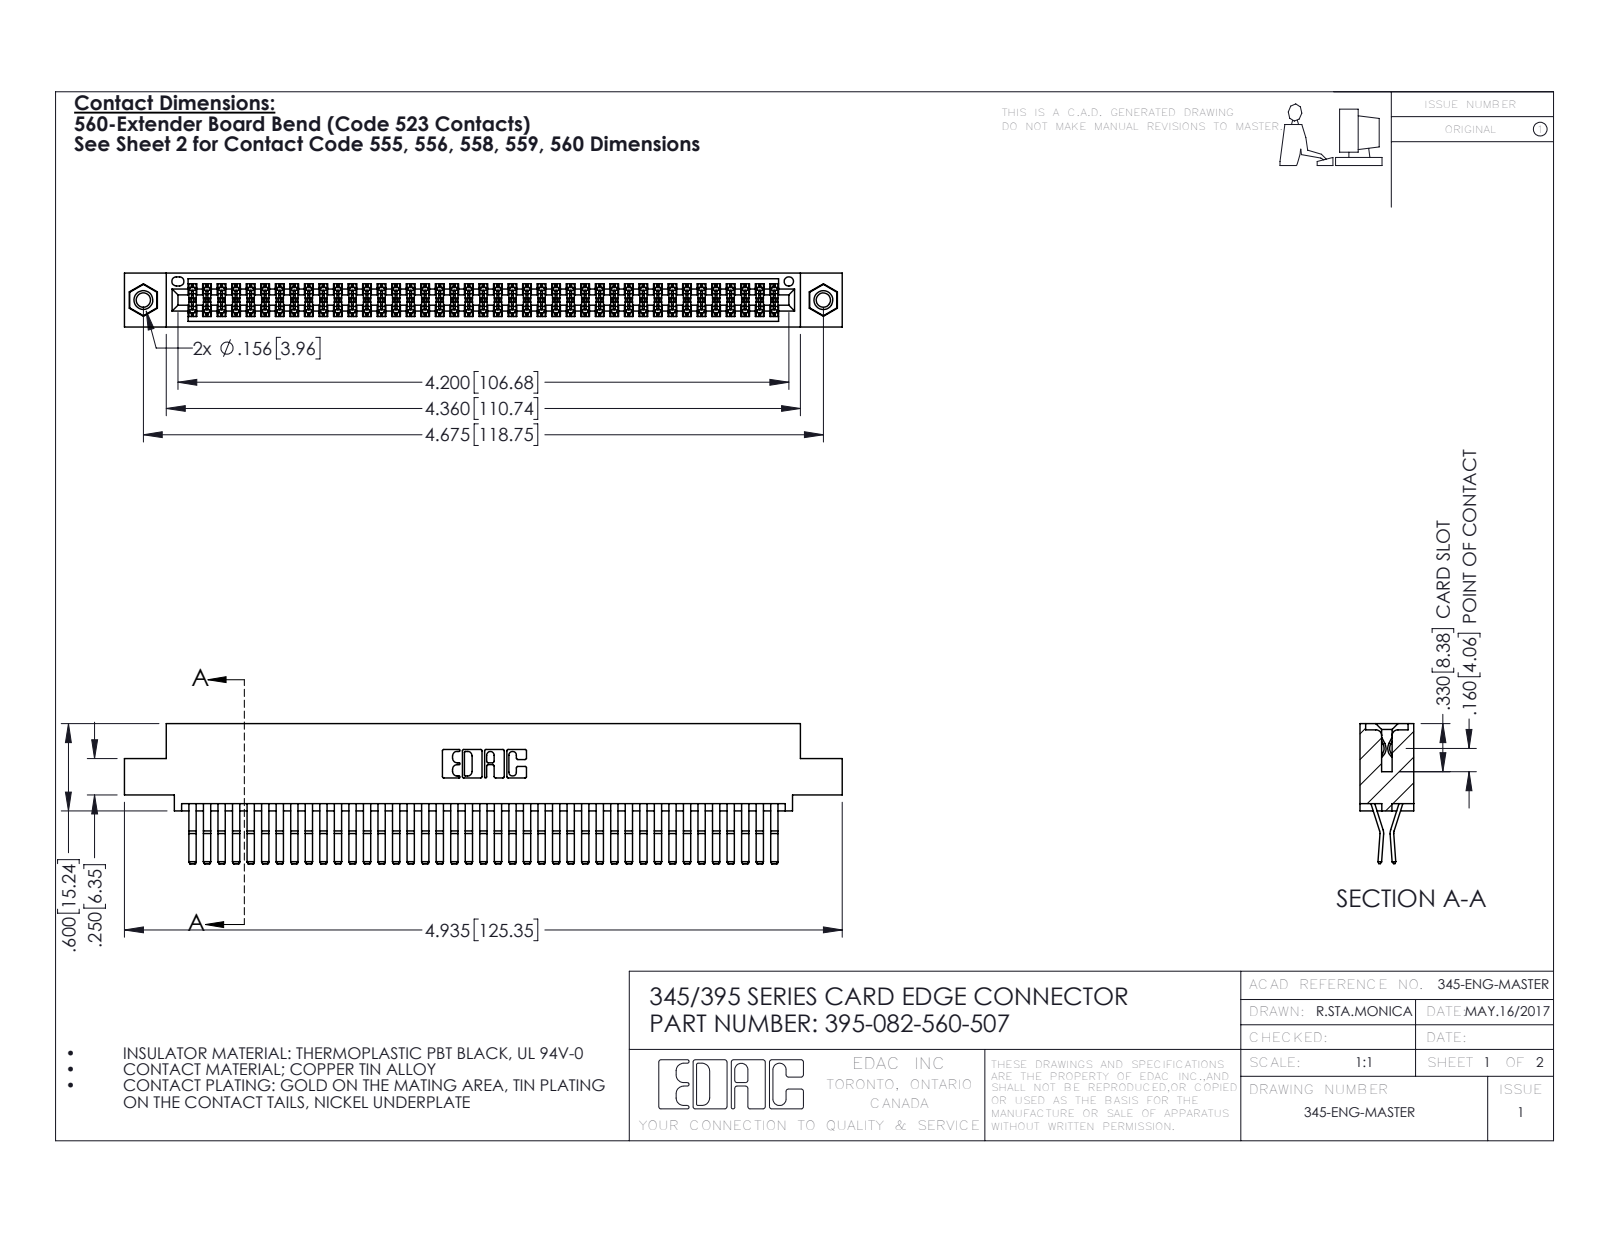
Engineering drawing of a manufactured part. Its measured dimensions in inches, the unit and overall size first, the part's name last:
Units: inches
Overall size (bounding box): 4.935 × 0.962 × 0.37
Round holes (diameter × count): ⌀0.098 ×2, ⌀0.125 ×2, ⌀0.156 ×2, ⌀0.064 ×1
Round bosses / shafts (diameter × count): ⌀0.155 ×2
Partial cylindrical surfaces — rounded edges, fillets, slot ends (radius × count): R0.006 ×123, R0.01 ×22, R0.007 ×6, R0.031 ×6, R0.026 ×3, R0.01 ×2, R0.014 ×2, R0.019 ×2
Main face-to-face distances: 0.025, 0.072, 0.298, 0.37, 0.2, 0.098, 0.272, 0.225, 0.175, 0.149
Hole centre spacings: 0.27, 4.439, 4.675
Volume: 0.77 in³ · Surface area: 31.21 in²
Bodies: 85 solids, 4454 faces (2822 planar, 1616 cylindrical, 16 other)
Part name (STEP PRODUCT): 345 Part_0.110 Offset - 0.156 Dia-TI; 395-082-560-507; 345-292-001_560 Tail; 345-250-001_345-250-005-103
STEP written by: SolidWorks 2016 (CONFIG_CONTROL_DESIGN)
